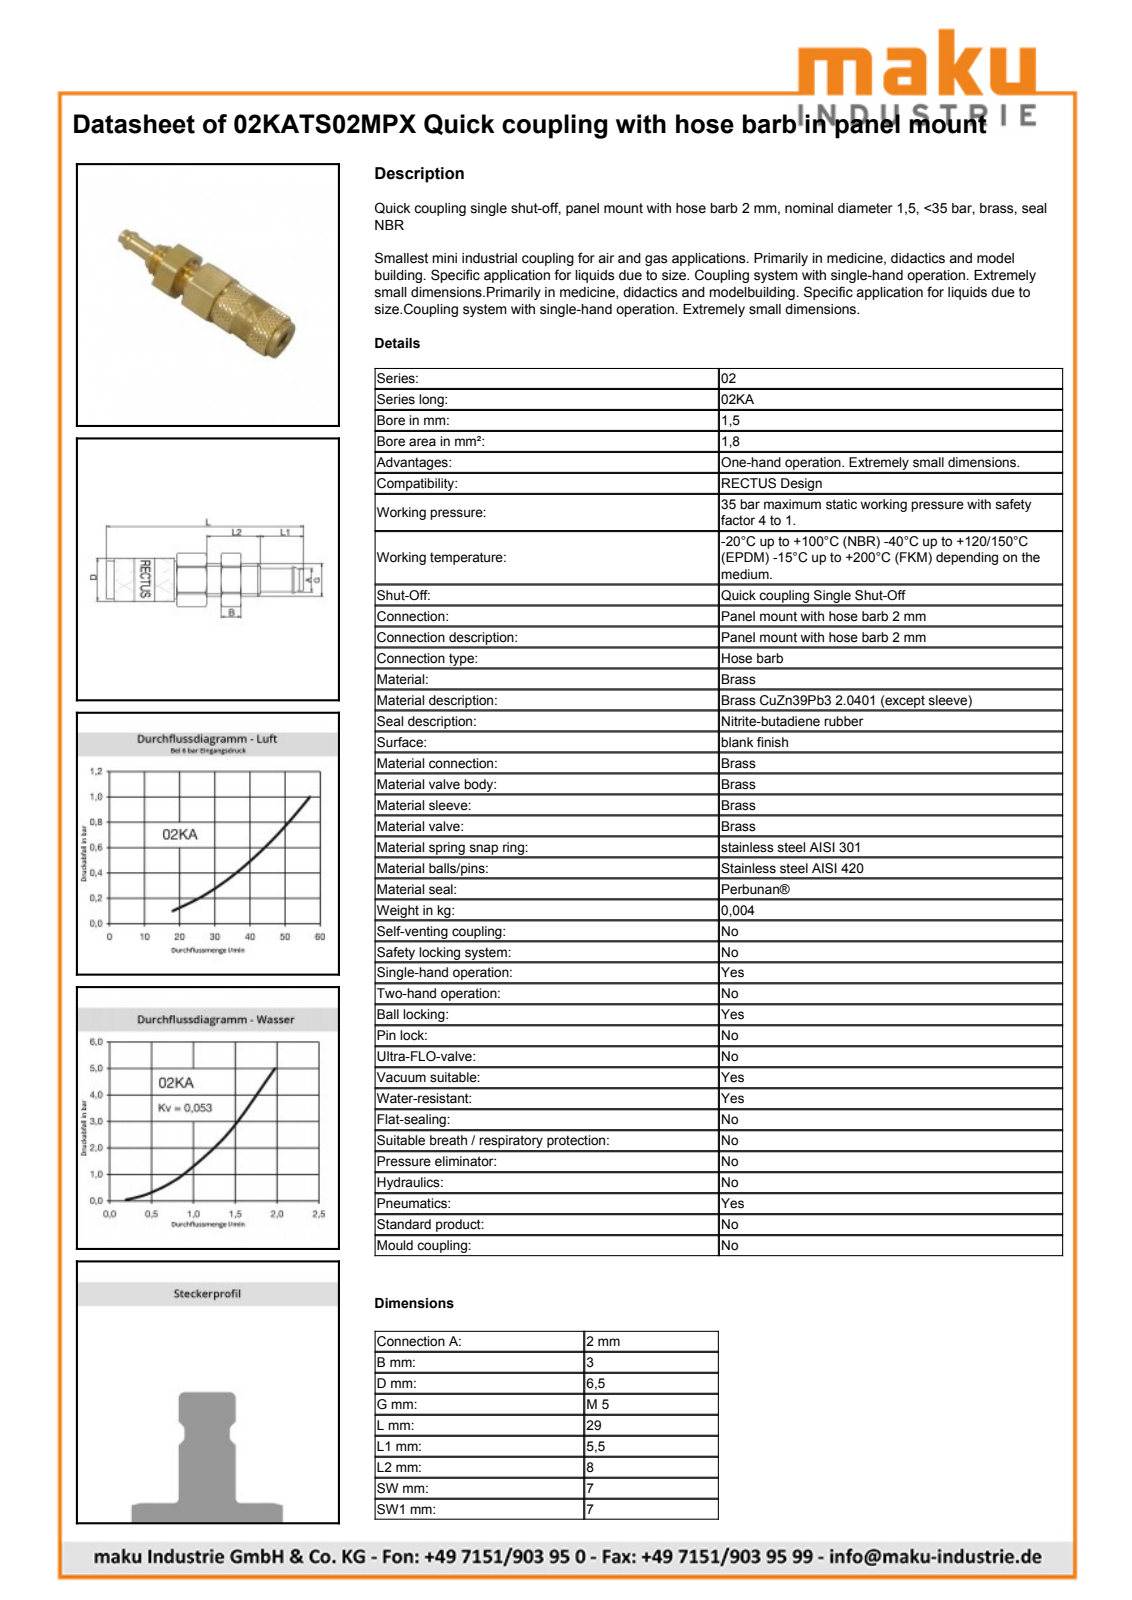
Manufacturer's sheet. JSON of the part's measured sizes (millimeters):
{"part_name": "D107887", "step_written_by": "Autodesk Inventor 2013 (AUTOMOTIVE_DESIGN)", "units": "millimeters", "bodies": {"solids": 2, "faces": 305, "planar": 97, "cylindrical": 55, "other": 153}, "overall_size": [28.5, 7.86, 7.63], "volume_mm3": 710, "surface_area_mm2": 1051, "round_holes": [[4.5, 1], [5.15, 1], [5.75, 1], [5.8, 1]], "round_bosses_or_shafts": [[6.5, 1], [6.3, 1], [5.7, 1], [5.6, 1], [5, 1], [4.4, 1], [4.25, 1], [4, 1]], "partial_cylinders_radius": [[3.05, 1], [3.95, 1]], "face_to_face_distances": [7, 3, 15, 4.5, 20.16, 5.16, 17.16, 2.16, 2, 10.5]}
